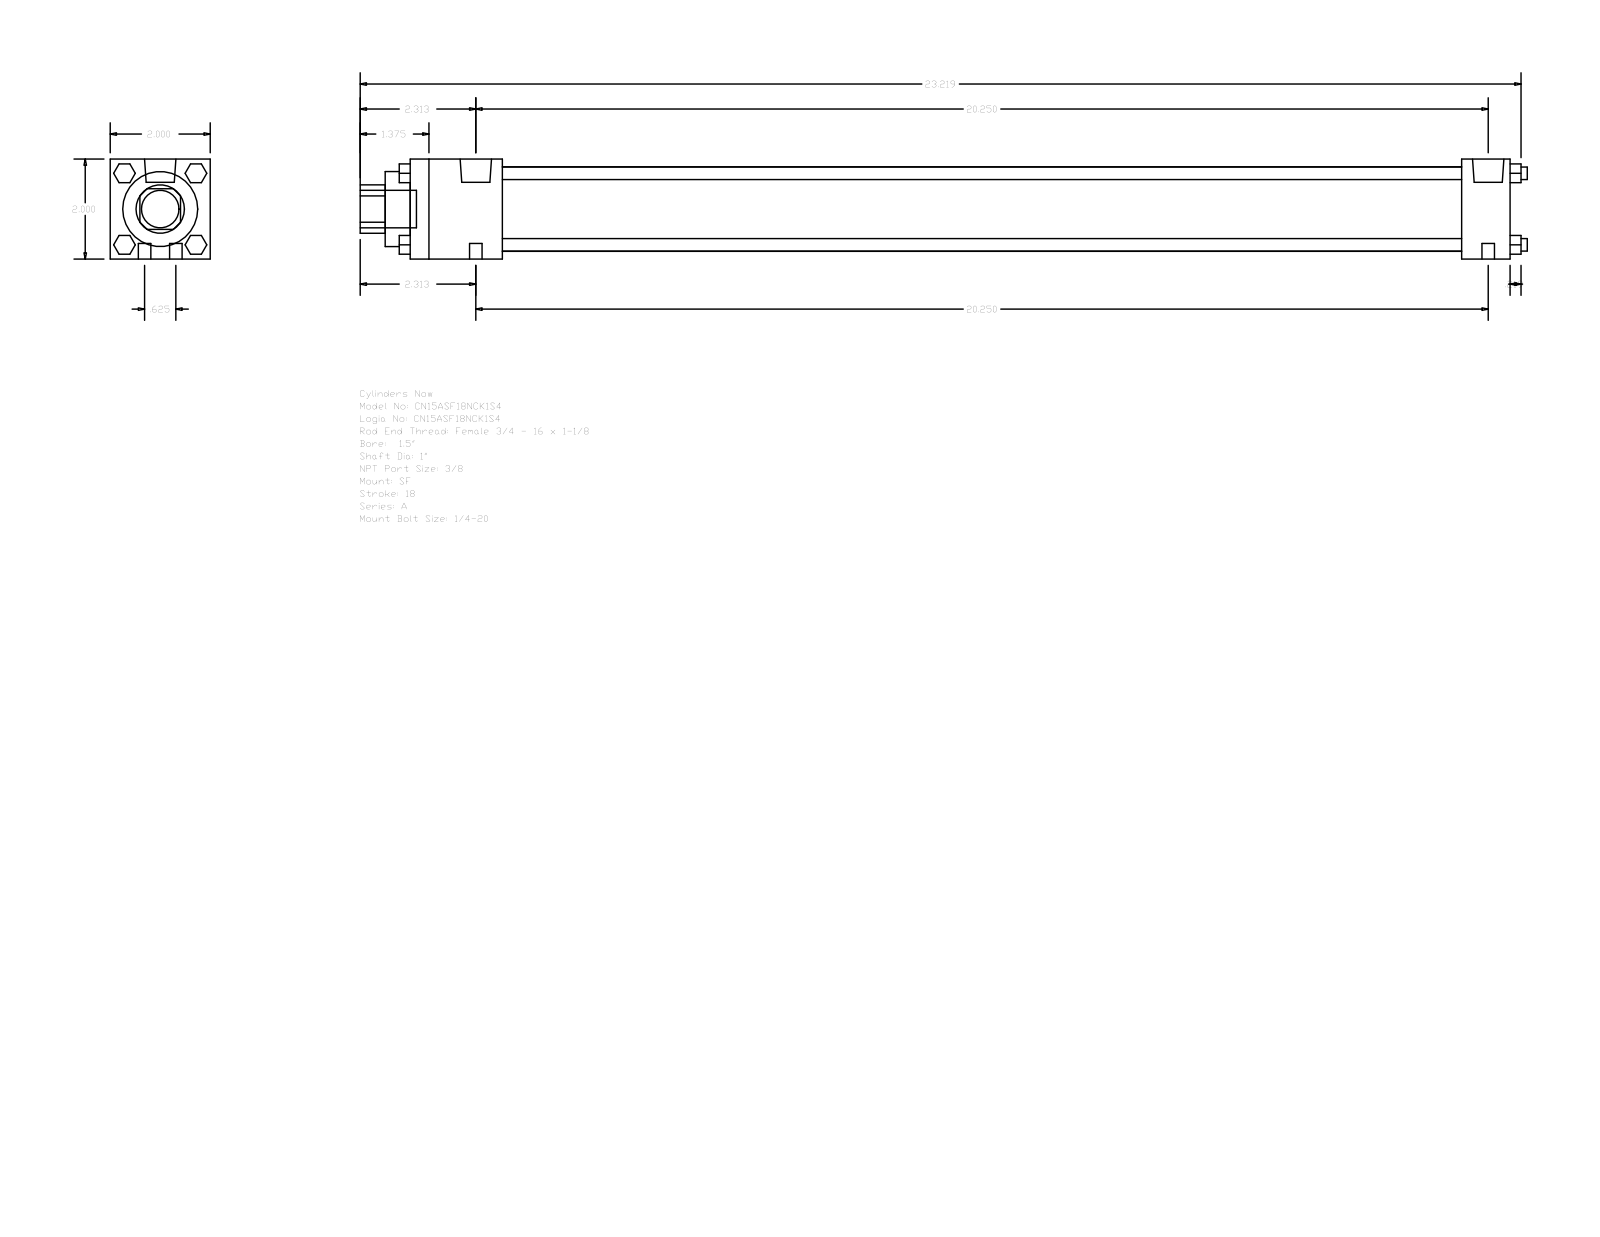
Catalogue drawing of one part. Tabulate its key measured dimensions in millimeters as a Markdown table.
| quantity | value |
| --- | --- |
| part name | A_SF__0150_1 |
| STEP written by | GSSL Pune (CONFIG_CONTROL_DESIGN) |
| units | millimeters |
| bodies | 0 solids, 124 faces (94 planar, 30 cylindrical, 0 other) |
| overall size | 592.93 × 50.8 × 50.8 |
| round holes (diameter × count) | 25.4 × 1, 38.1 × 1, 42.93 × 1 |
| round bosses / shafts (diameter × count) | 6.35 × 8, 15.93 × 2, 5.56 × 2, 19.05 × 1 |
| partial cylindrical surfaces (radius × count) | 12.29 × 1 |
| main face-to-face distances | 50.8, 558.8, 46.83, 534.19, 487.36, 511.97, 24.61, 12.7, 59.53, 546.89 |
